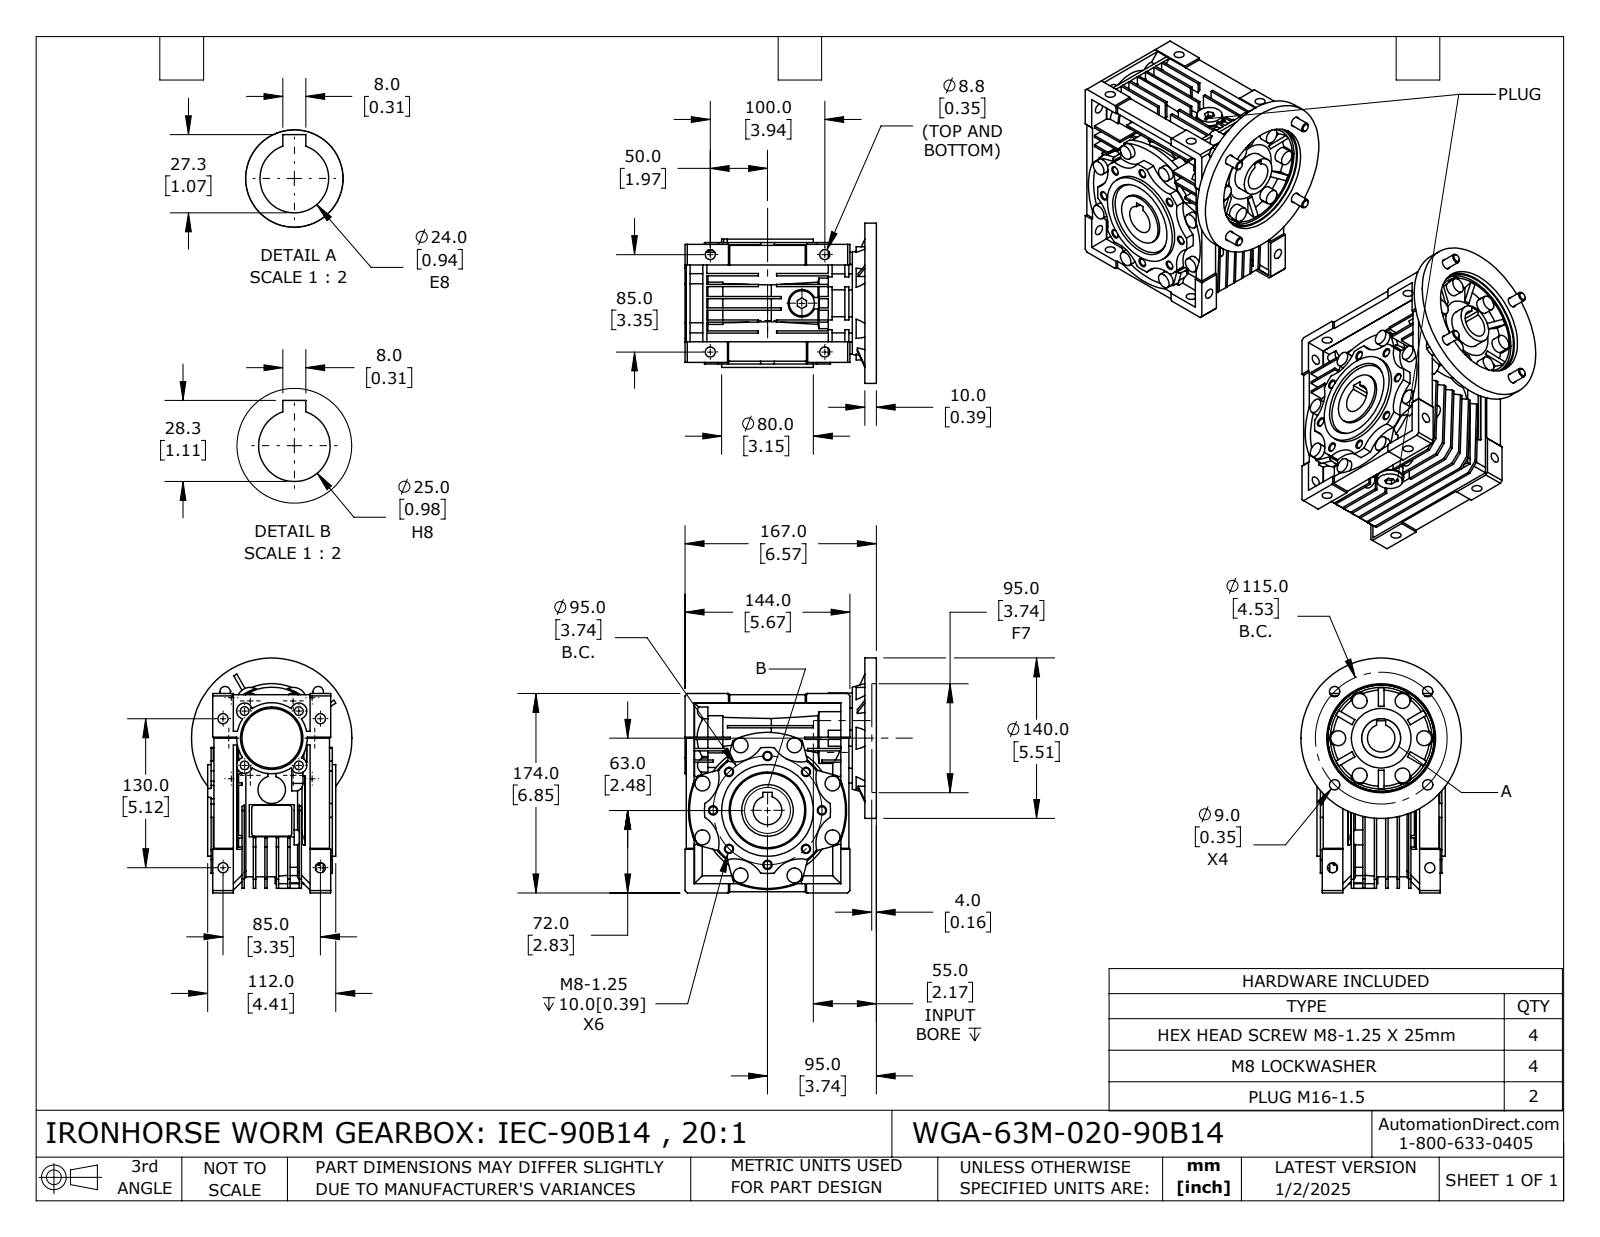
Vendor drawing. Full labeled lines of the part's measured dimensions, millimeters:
Part name (STEP PRODUCT): WGA-63M-020-90B14
STEP written by: SolidWorks 2024 (CONFIG_CONTROL_DESIGN)
Units: millimetres
Bodies: 16 solids, 1375 faces (833 planar, 365 cylindrical, 177 other)
Overall size (bounding box): 205 × 180 × 140
Volume: 1 870 000 mm³ · Surface area: 362 276 mm²
Round holes (diameter × count): ⌀6.65 ×8, ⌀8.78 ×8, ⌀7.56 ×4, ⌀8.2 ×4, ⌀9 ×4, ⌀14.5 ×2, ⌀25 ×2, ⌀24 ×1, ⌀34 ×1, ⌀37 ×1, ⌀45 ×1, ⌀52 ×1
Round bosses / shafts (diameter × count): ⌀13 ×14, ⌀15.4 ×4, ⌀8 ×4, ⌀24 ×3, ⌀22 ×2, ⌀15.8 ×2, ⌀13.7 ×2, ⌀140 ×1
Partial cylindrical surfaces — rounded edges, fillets, slot ends (radius × count): R7 ×10, R27 ×8, R7.5 ×6, R11.9 ×6, R2.5 ×4, R8.35 ×1, R29.5 ×1, R30.5 ×1
Main face-to-face distances: 10, 8, 20, 2, 30, 12, 7, 18, 40, 21
Hole centre spacings: 36.36, 47.5, 66.55, 67.18, 87.77, 24, 33.5, 47.38
